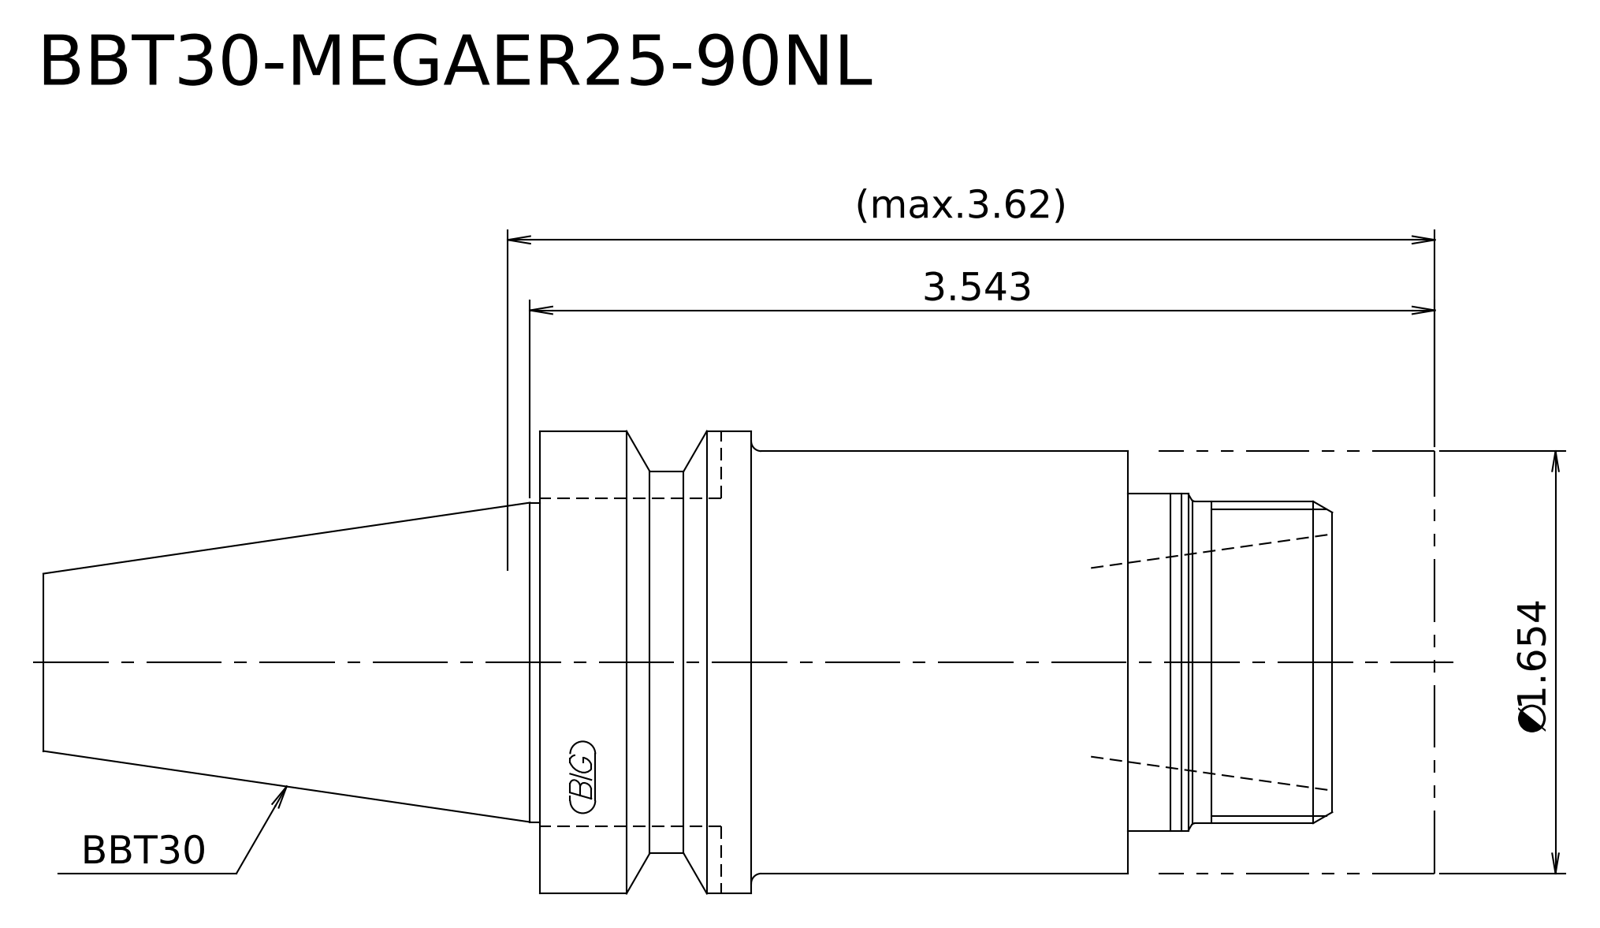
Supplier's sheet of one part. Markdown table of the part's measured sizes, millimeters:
| quantity | value |
| --- | --- |
| STEP written by | Kubotek KeyCreator 2011 V10.0.2 (22737) (automotive_design) |
| units | millimeters |
| bodies | 2 solids, 21 faces (7 planar, 8 cylindrical, 6 other) |
| overall size | 138.4 × 46 × 46 |
| volume | 163 278 mm³ |
| surface area | 23 395 mm² |
| round bosses / shafts (diameter × count) | 46 × 1, 42 × 1, 38 × 1, 33.5 × 1, 32 × 1, 31.75 × 1 |
| main face-to-face distances | 27.5, 89, 61.5, 10.2, 17.3, 78.8, 30.5, 20.3, 3, 58.5 |
